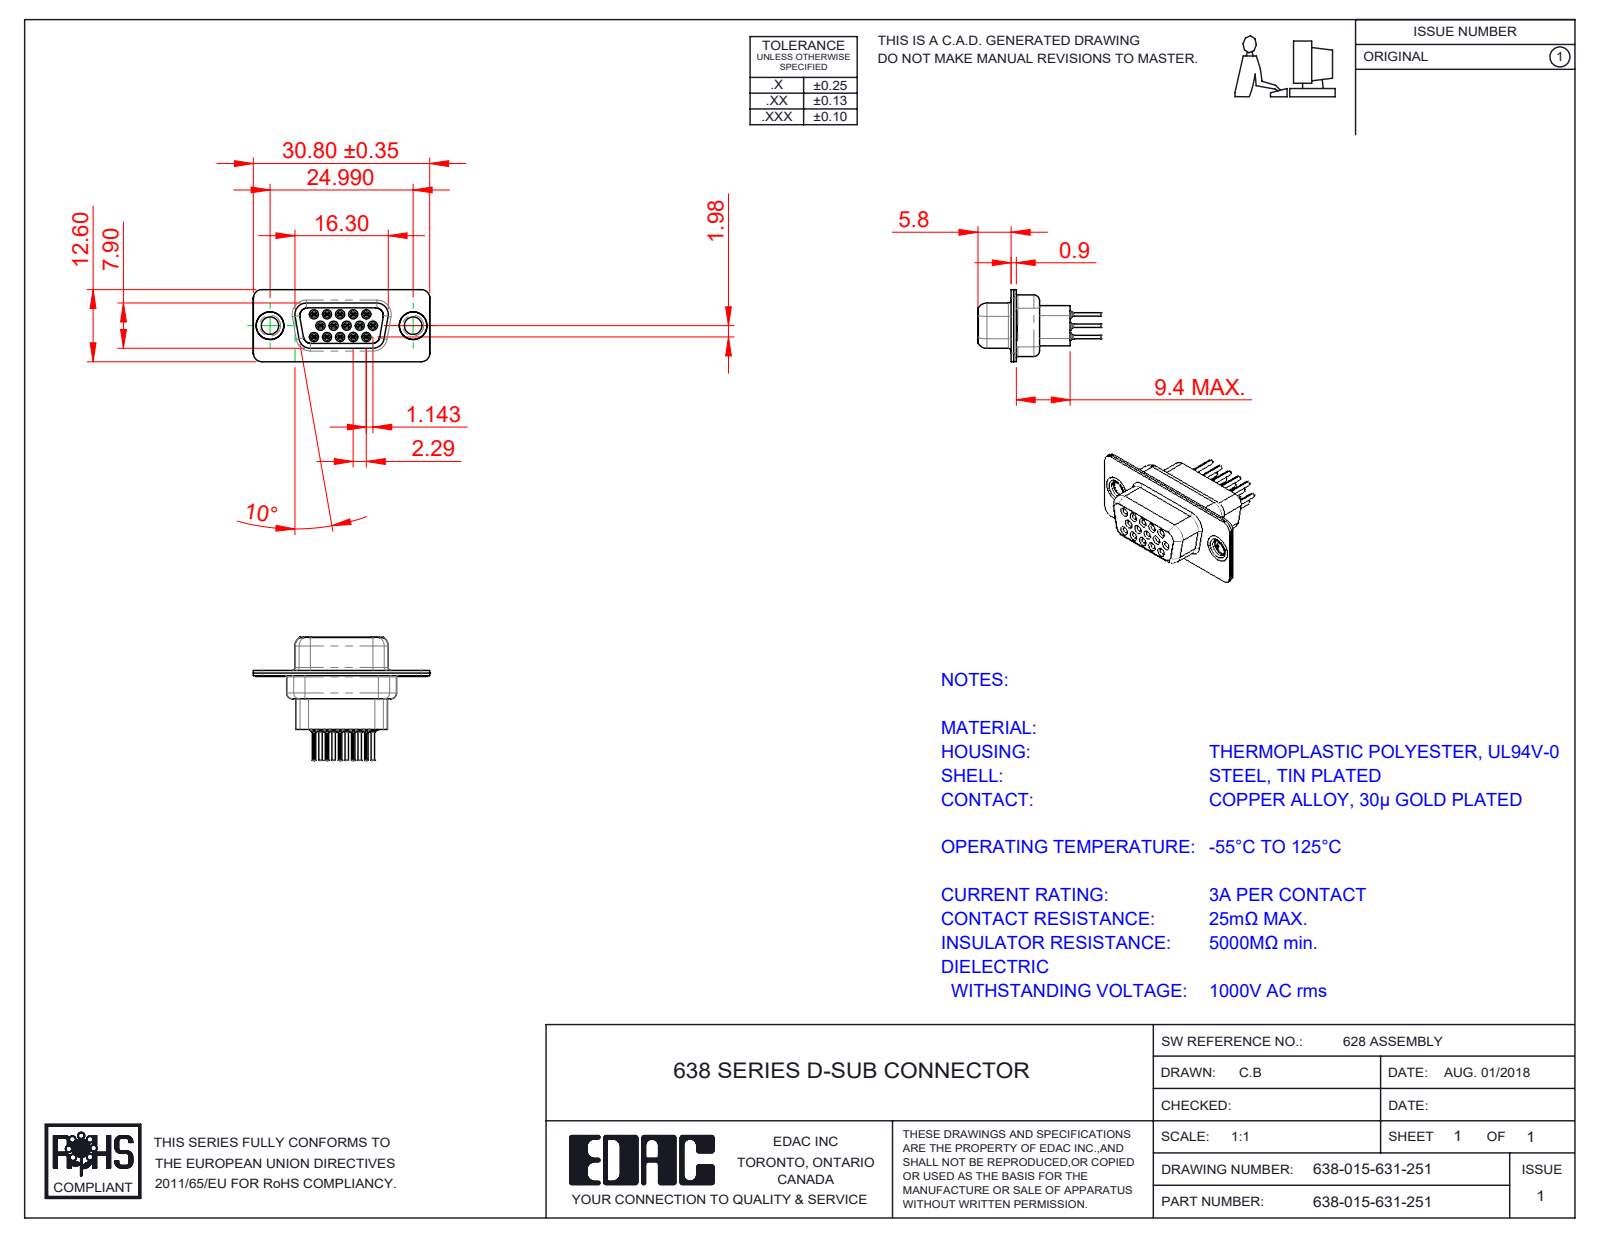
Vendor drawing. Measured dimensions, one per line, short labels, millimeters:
name: 638-015-631-251; 638 Contact Row 1_31; 638 Housing_15 Contacts HP; 638 Contact Row 2_31 (+4 more)
written by: SolidWorks 2020 (CONFIG_CONTROL_DESIGN)
unit: mm
bodies: 20 solids, 2098 faces (532 planar, 616 cylindrical, 950 other)
size: 30.81 × 21.5 × 12.6
volume: 1 805 mm³; area: 6 385 mm²
holes: 15× ⌀0.2, 15× ⌀0.8, 15× ⌀1, 15× ⌀1.1, 15× ⌀1.6, 15× ⌀1.7, 15× ⌀1.8, 2× ⌀2, 2× ⌀3.05, 2× ⌀4, 2× ⌀4.05, 2× ⌀4.85
bosses: 15× ⌀2, 15× ⌀1.5, 15× ⌀1.2, 15× ⌀0.6, 2× ⌀5, 2× ⌀4.95, 2× ⌀4.8, 2× ⌀3.55
rounds: 30× R0.1, 20× R1.5, 12× R2, 10× R0.28, 8× R1.55, 5× R1.35, 4× R0.25, 4× R0.5
face distances: 0.45, 0.9, 0.4, 1.43, 8.88, 6.6, 7, 2.28, 5.8, 6.2
hole spacings: 3.96, 2.28, 4.57, 2.29, 6.05, 6.04, 6.86, 7.92
